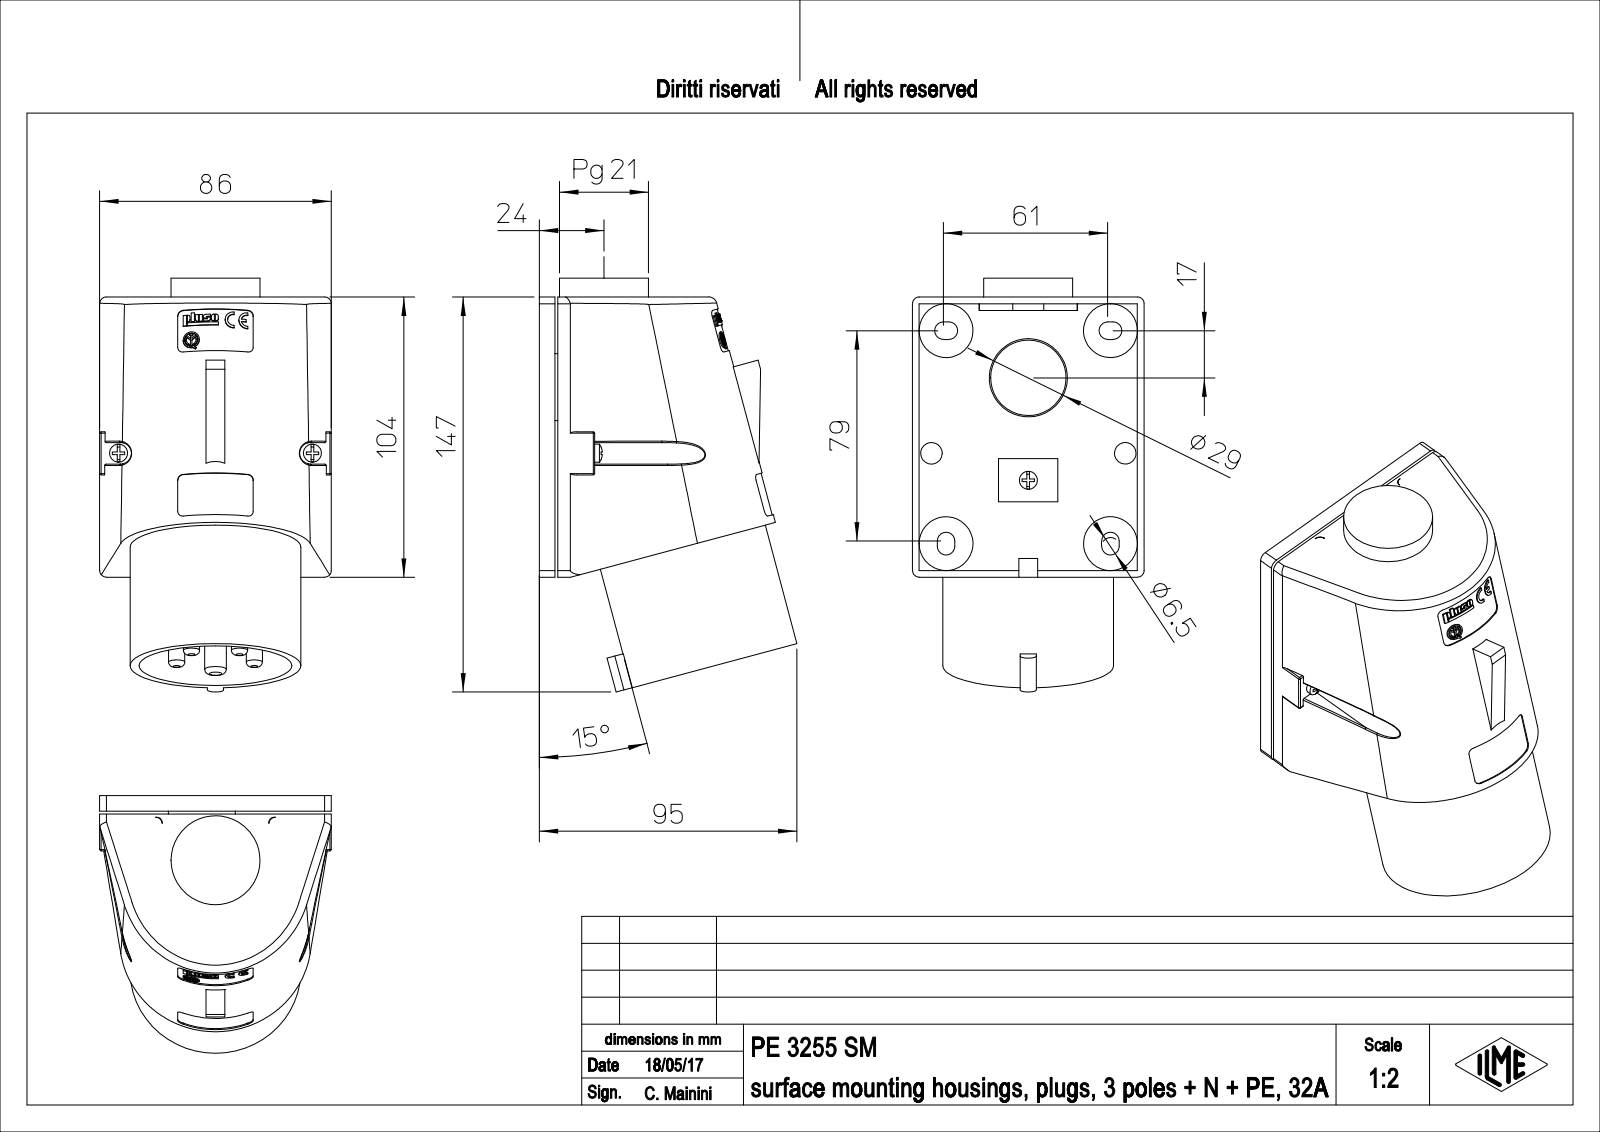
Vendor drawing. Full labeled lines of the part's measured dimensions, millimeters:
Part name (STEP PRODUCT): PE_3255_SM
STEP written by: PTC Creo Elements/Direct Modeling 19.0E 27-Jun-2016 (C) Parametric Technology GmbH (AUTOMOTIVE_DESIGN)
Units: millimetres
Bodies: 1 solid, 1055 faces (668 planar, 220 cylindrical, 167 other)
Overall size (bounding box): 153.55 × 95.62 × 86
Volume: 518 948 mm³ · Surface area: 96 274 mm²
Round holes (diameter × count): ⌀6.1 ×4, ⌀2.8 ×2, ⌀3.2 ×2, ⌀4 ×2, ⌀4.5 ×2, ⌀4.2 ×1, ⌀5.04 ×1, ⌀27.54 ×1, ⌀29 ×1, ⌀32 ×1, ⌀56.7 ×1
Round bosses / shafts (diameter × count): ⌀6.7 ×5, ⌀6 ×5, ⌀20 ×4, ⌀8 ×3, ⌀3 ×2, ⌀63.4 ×1, ⌀33 ×1, ⌀24.84 ×1
Partial cylindrical surfaces — rounded edges, fillets, slot ends (radius × count): R0.5 ×20, R0.17 ×11, R2 ×10, R0.86 ×9, R3.25 ×8, R2.5 ×6, R0.75 ×4, R4.5 ×4
Main face-to-face distances: 1.07, 4.75, 5.82, 7, 1, 5.75, 6.82, 2.25, 2.5, 8
Hole centre spacings: 15.15, 72, 17.81, 21.93, 24.8, 28.81, 37.36, 37.37
